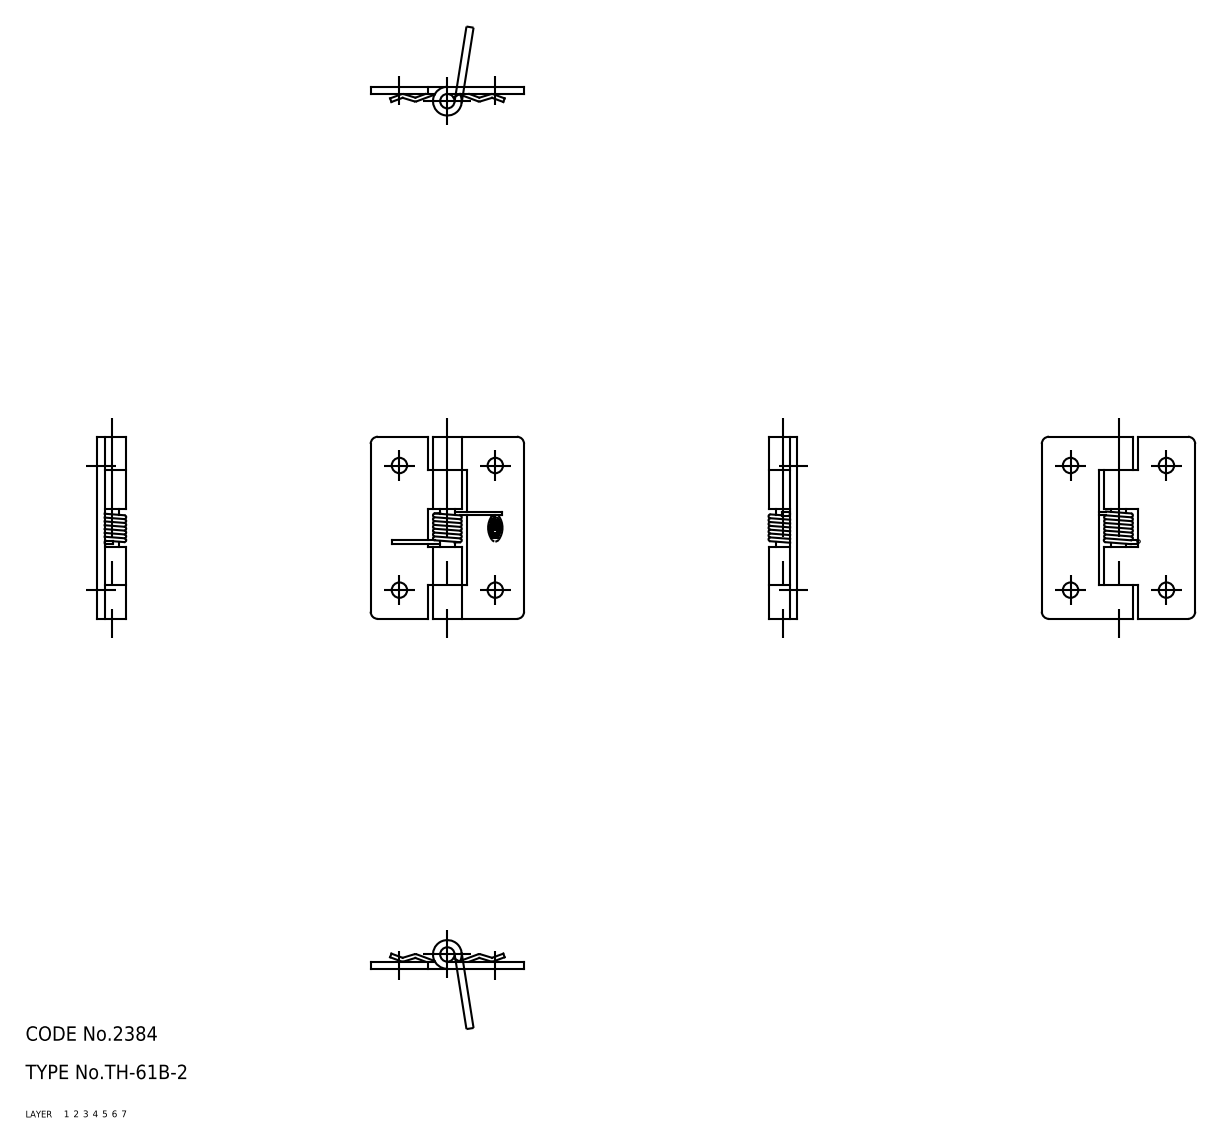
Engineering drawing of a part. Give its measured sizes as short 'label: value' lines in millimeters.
name: spring; shaft; hinge piece_B; hinge piece_A (+1 more)
written by: CADfix (AUTOMOTIVE_DESIGN)
unit: mm
bodies: 4 solids, 77 faces (0 planar, 0 cylindrical, 77 other)
size: 38 × 32 × 6
volume: 2 357 mm³; area: 3 930 mm²
